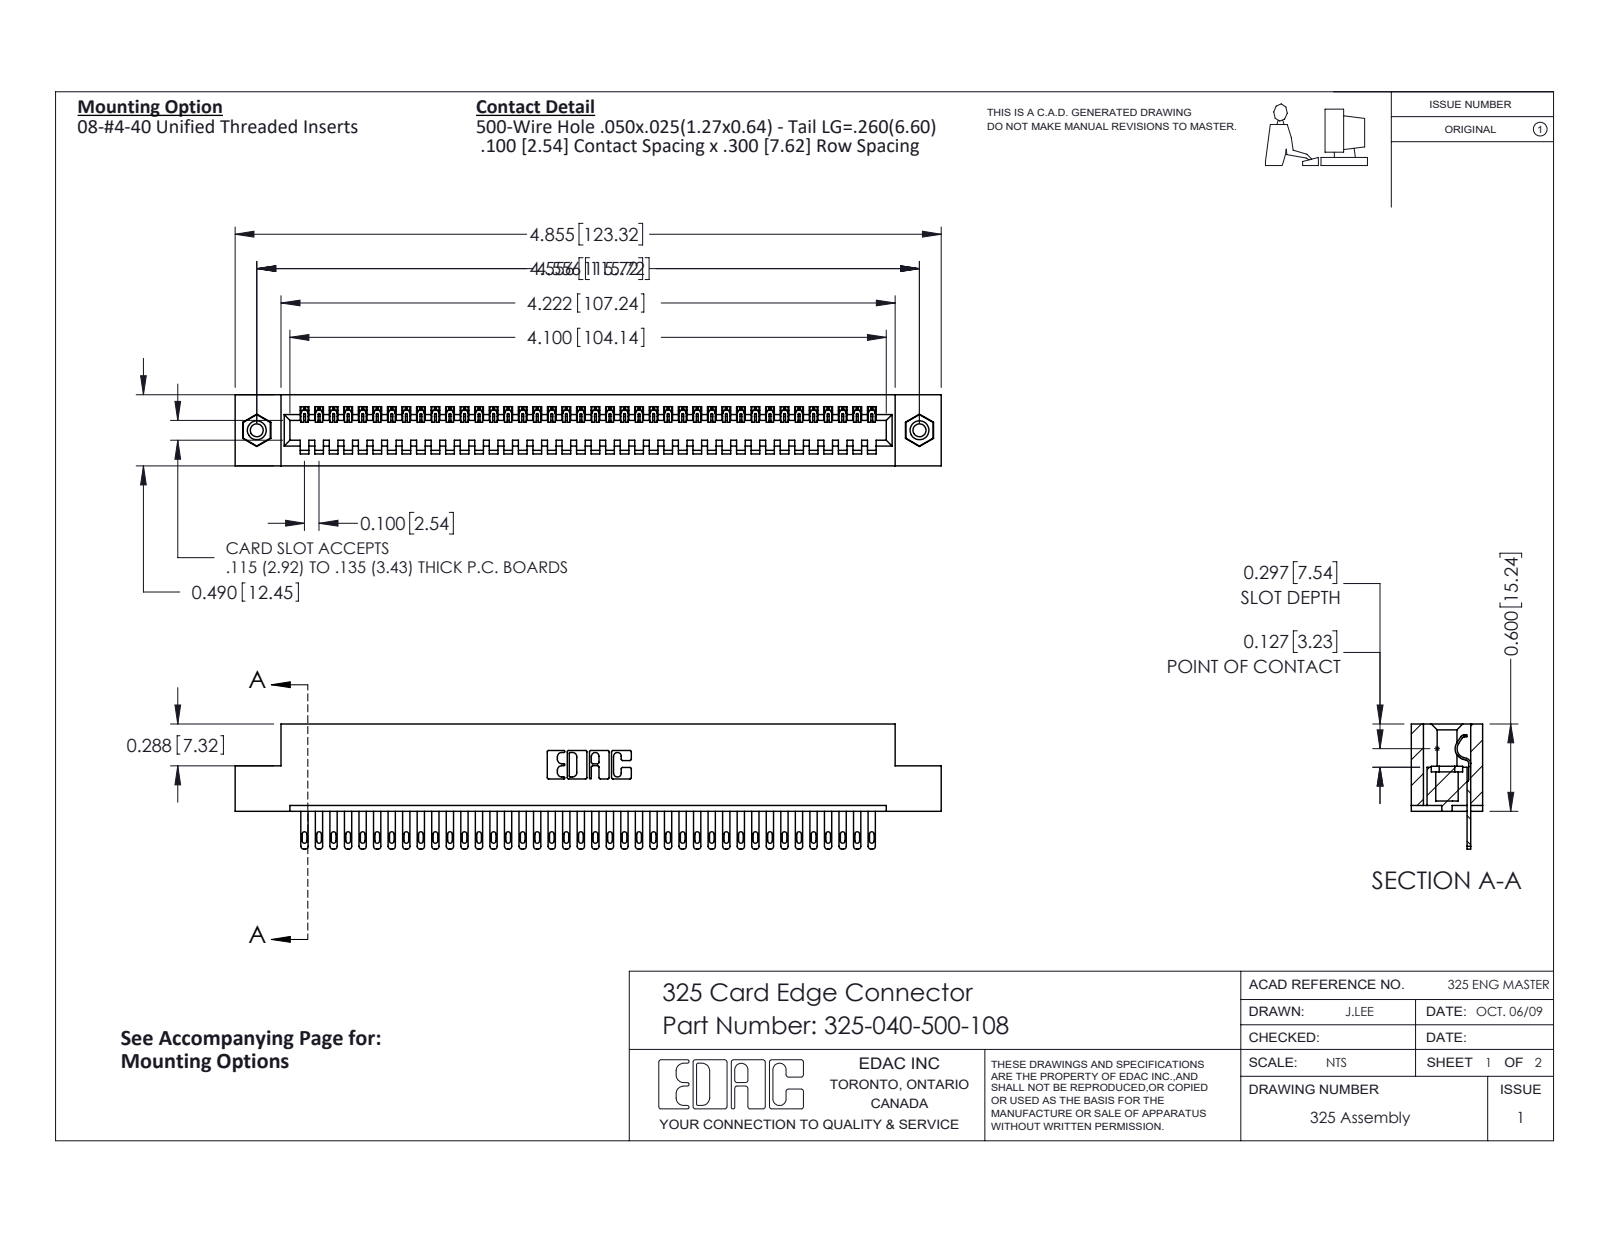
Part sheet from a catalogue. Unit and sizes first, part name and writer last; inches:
Units: inches
Overall size (bounding box): 4.855 × 0.86 × 0.49
Round holes (diameter × count): ⌀0.089 ×2, ⌀0.125 ×2, ⌀0.16 ×2
Round bosses / shafts (diameter × count): ⌀0.155 ×2
Partial cylindrical surfaces — rounded edges, fillets, slot ends (radius × count): R0.006 ×80, R0.016 ×80, R0.02 ×80, R0.01 ×22, R0.007 ×6, R0.031 ×6, R0.026 ×3, R0.014 ×1
Main face-to-face distances: 0.083, 0.407, 0.49, 0.3, 0.107, 0.383, 0.025, 0.325, 0.56, 0.263
Hole centre spacings: 4.556
Volume: 0.955 in³ · Surface area: 26.63 in²
Bodies: 43 solids, 2334 faces (1542 planar, 776 cylindrical, 16 other)
Part name (STEP PRODUCT): 345-250-001_345-250-003-102; 325-040-500-108; 325 Part_TI; 325-292-001_325-293-100
STEP written by: SolidWorks 2016 (CONFIG_CONTROL_DESIGN)
